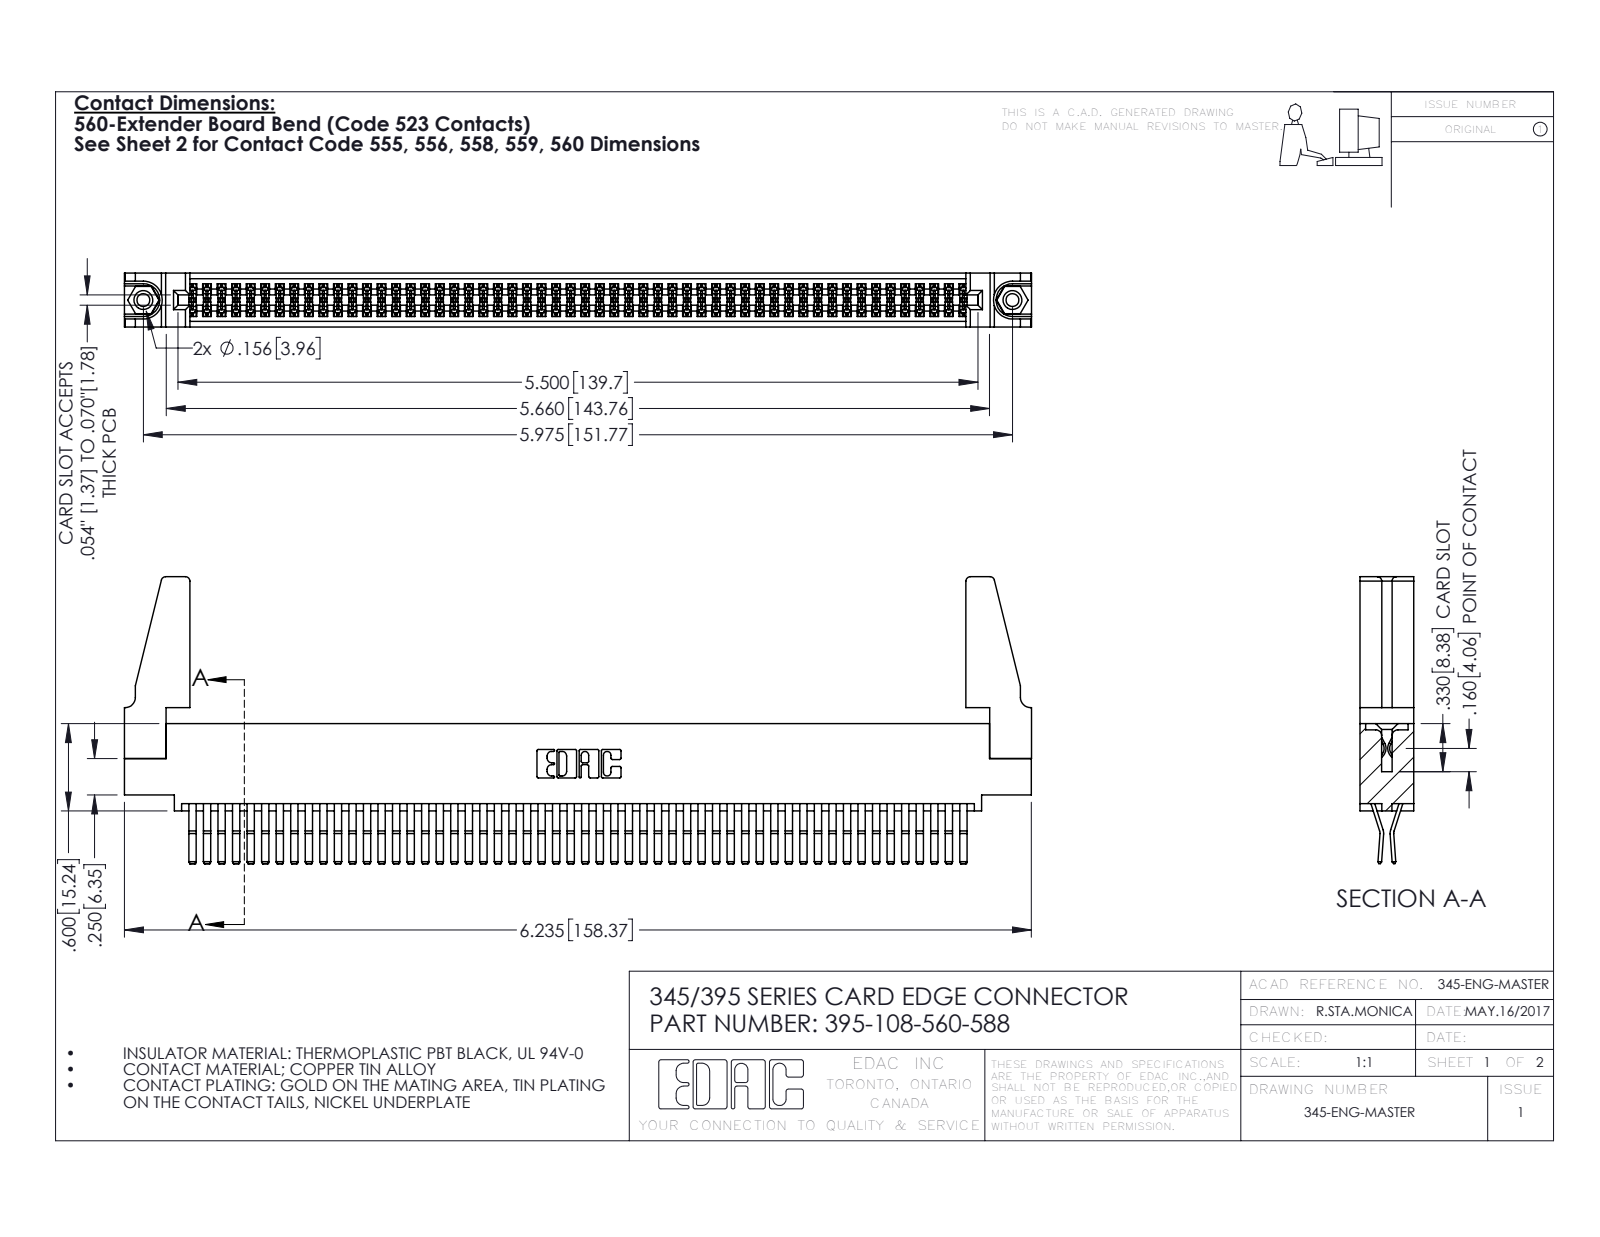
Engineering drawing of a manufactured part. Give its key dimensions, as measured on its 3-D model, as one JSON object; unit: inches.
{"part_name": "345 Part_0.110 Offset - 0.156 Dia-TH; 345-250-001_345-250-001-102; 395-108-560-588; 345-220-078_345-220-088 (+1 more)", "step_written_by": "SolidWorks 2016 (CONFIG_CONTROL_DESIGN)", "units": "inches", "bodies": {"solids": 113, "faces": 5870, "planar": 3720, "cylindrical": 2134, "other": 16}, "overall_size": [6.236, 1.972, 0.37], "volume_in3": 1.183, "surface_area_in2": 45.13, "round_holes": [[0.089, 2], [0.125, 2], [0.156, 2], [0.064, 1]], "round_bosses_or_shafts": [[0.155, 2]], "partial_cylinders_radius": [[0.006, 162], [0.01, 22], [0.03, 8], [0.007, 6], [0.031, 6], [0.026, 3], [0.01, 2], [0.014, 2]], "face_to_face_distances": [0.072, 0.298, 0.025, 0.37, 0.2, 0.098, 0.272, 0.225, 0.175, 0.149], "hole_center_spacings": [0.27, 5.739, 5.975]}
